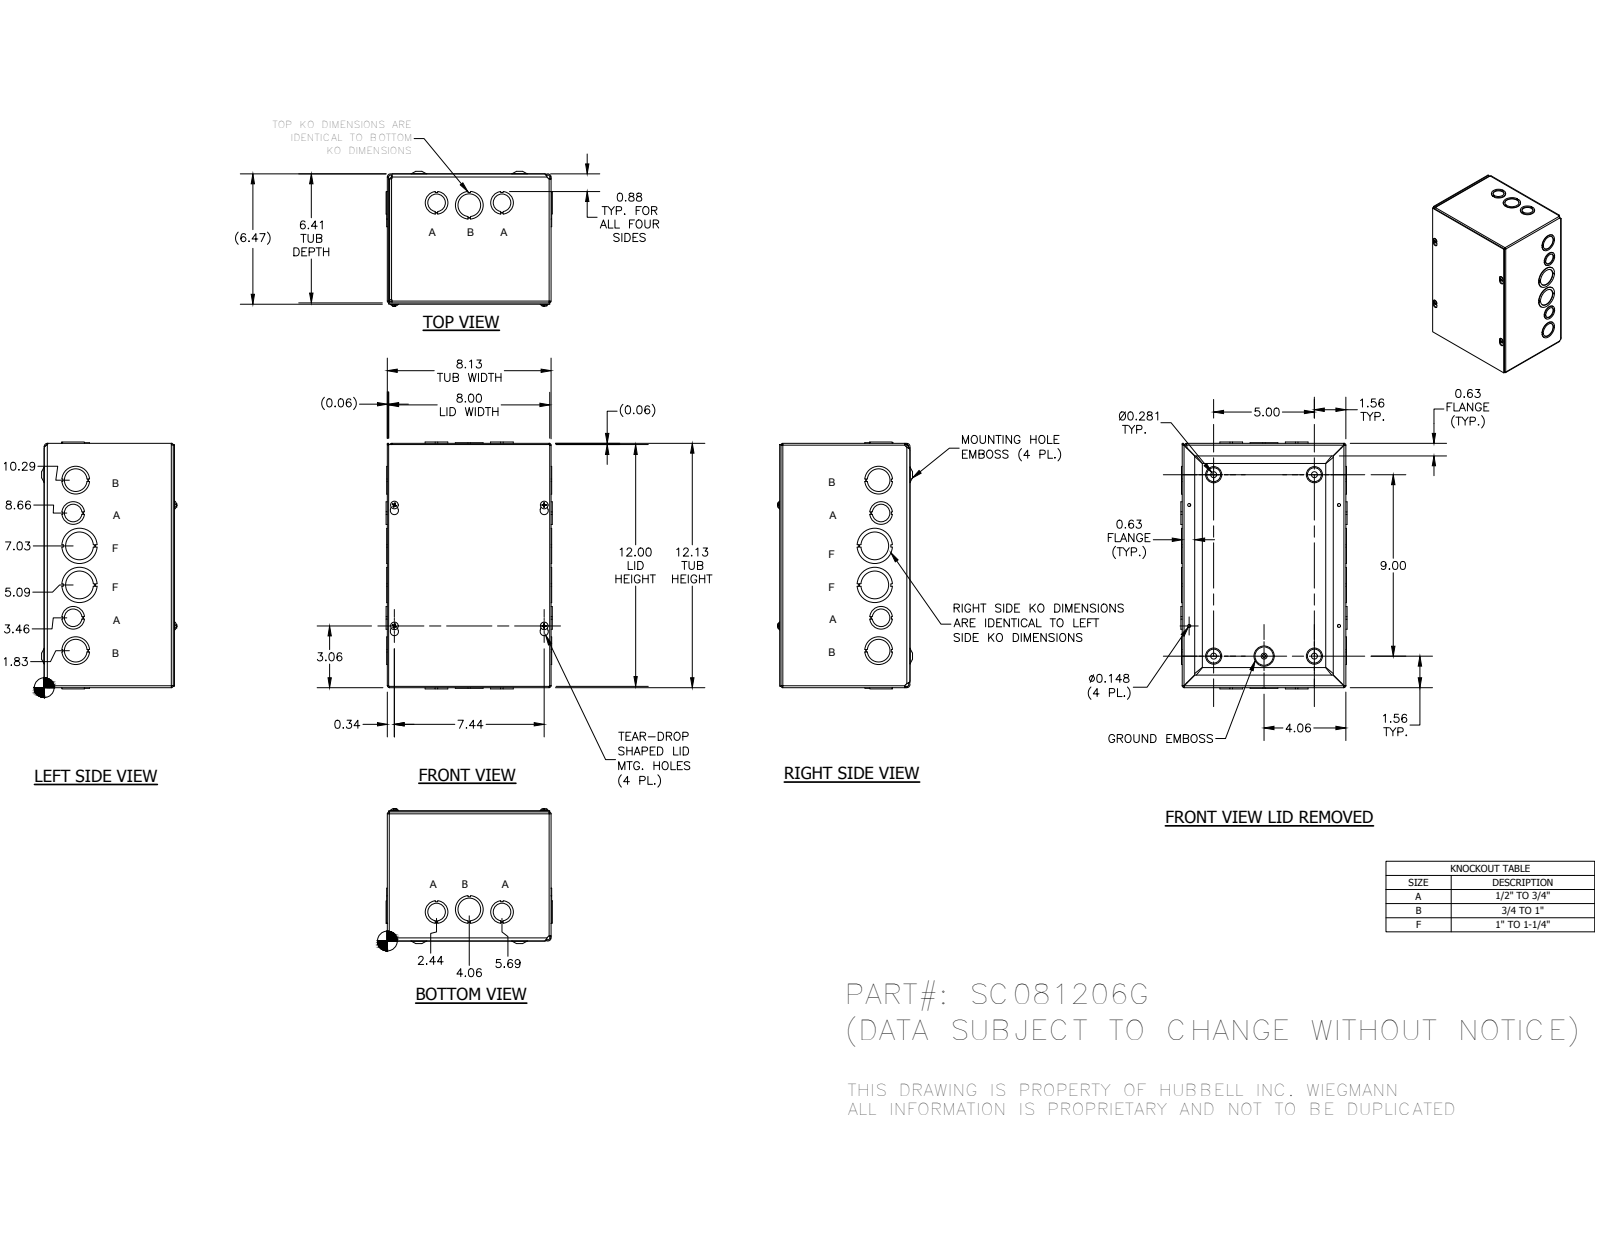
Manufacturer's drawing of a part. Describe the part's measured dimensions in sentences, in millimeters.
The part is named "SC0812GBKP; SC081206GWRA; SC0812GLID; 34056 (+1 more)". Its 3-D file was written by "Autodesk Inventor 2014 (AUTOMOTIVE_DESIGN)". It is 22 solids with 862 faces: 530 planar, 181 cylindrical and 151 other. Overall it measures 311.12 by 209.53 by 170 millimeters. Round holes: 7 of diameter 28.57, 5 of diameter 34.92, 4 of diameter 3.76, 4 of diameter 7.62, 4 of diameter 22.22, 2 of diameter 44.45, 1 of diameter 4.19. Round bosses or shafts: 4 of diameter 9.75, 4 of diameter 4.17, 1 of diameter 5.8. Partial cylindrical surfaces (rounded edges, fillets, slot ends): 8 of radius 0.79, 8 of radius 2.37, 4 of radius 1.4, 4 of radius 1.57, 4 of radius 2.38, 4 of radius 2.79, 4 of radius 2.97, 4 of radius 3.15. The main face-to-face distances are 1.57, 204.8, 161.12, 162.69, 1.59, 162.71, 164.28, 206.37, 1.58, 203.23. The hole center spacings are 49.09, 193, 41.52, 42.15, 63.5, 82.94, 91.03, 101.85.
